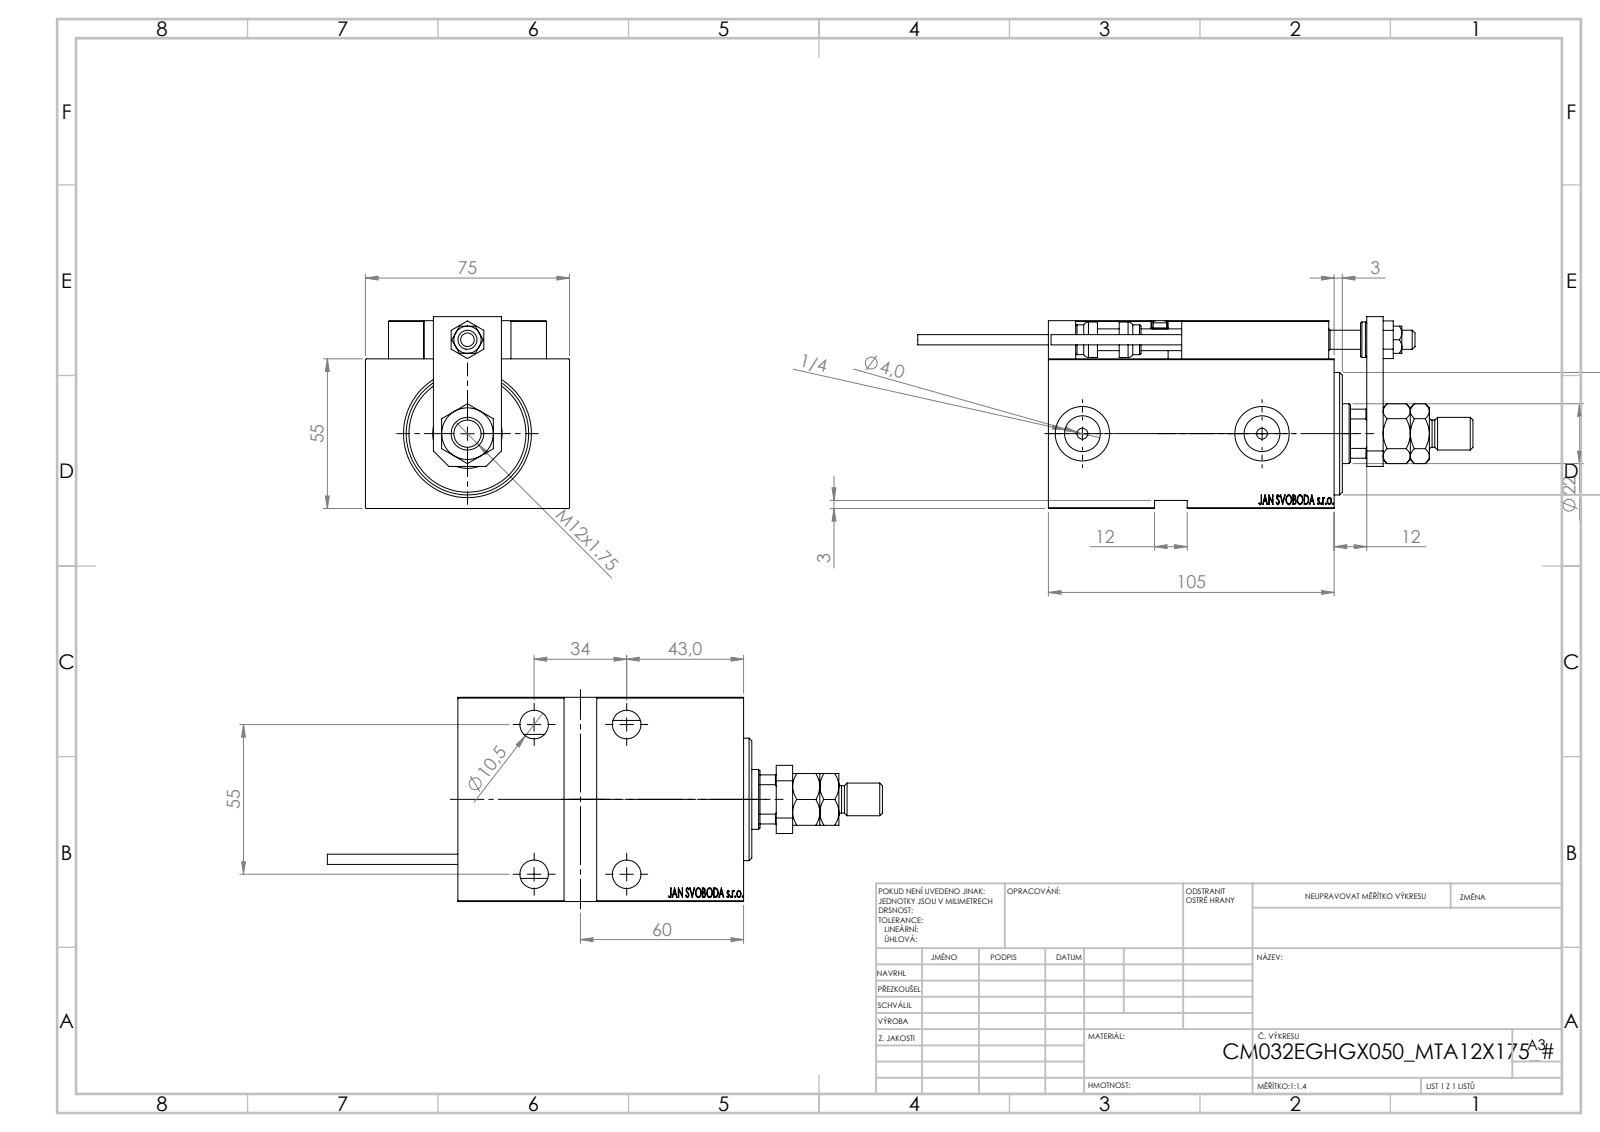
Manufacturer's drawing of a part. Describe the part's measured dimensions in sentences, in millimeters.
The part is named "NUT_D10; V450CM_E_Body; V450CM_VC_B; KONCOVKA (+7 more)". Its 3-D file was written by "SolidWorks 2019 (CONFIG_CONTROL_DESIGN)". It is 25 solids with 1342 faces: 585 planar, 186 cylindrical and 571 other. Overall it measures 204 by 75 by 70.5 millimeters. Its volume is 435 890 cubic millimeters and its surface area 98 534 square millimeters. Round holes: 6 of diameter 4, 5 of diameter 8, 5 of diameter 10.5, 5 of diameter 16.5, 4 of diameter 3.2, 2 of diameter 5, 2 of diameter 13.16, 2 of diameter 20, 1 of diameter 7, 1 of diameter 22, 1 of diameter 25.5, 1 of diameter 32. Round bosses or shafts: 2 of diameter 5, 2 of diameter 3.8, 1 of diameter 13, 1 of diameter 12, 1 of diameter 11, 1 of diameter 10. Partial cylindrical surfaces (rounded edges, fillets, slot ends): 30 of radius 0.3, 2 of radius 3, 1 of radius 10.5. The main face-to-face distances are 55, 75, 3, 10, 14, 69, 105, 12, 95, 18. The hole center spacings are 11.37, 20, 28.9, 29.59, 29.69, 34, 36.06, 40.03.
